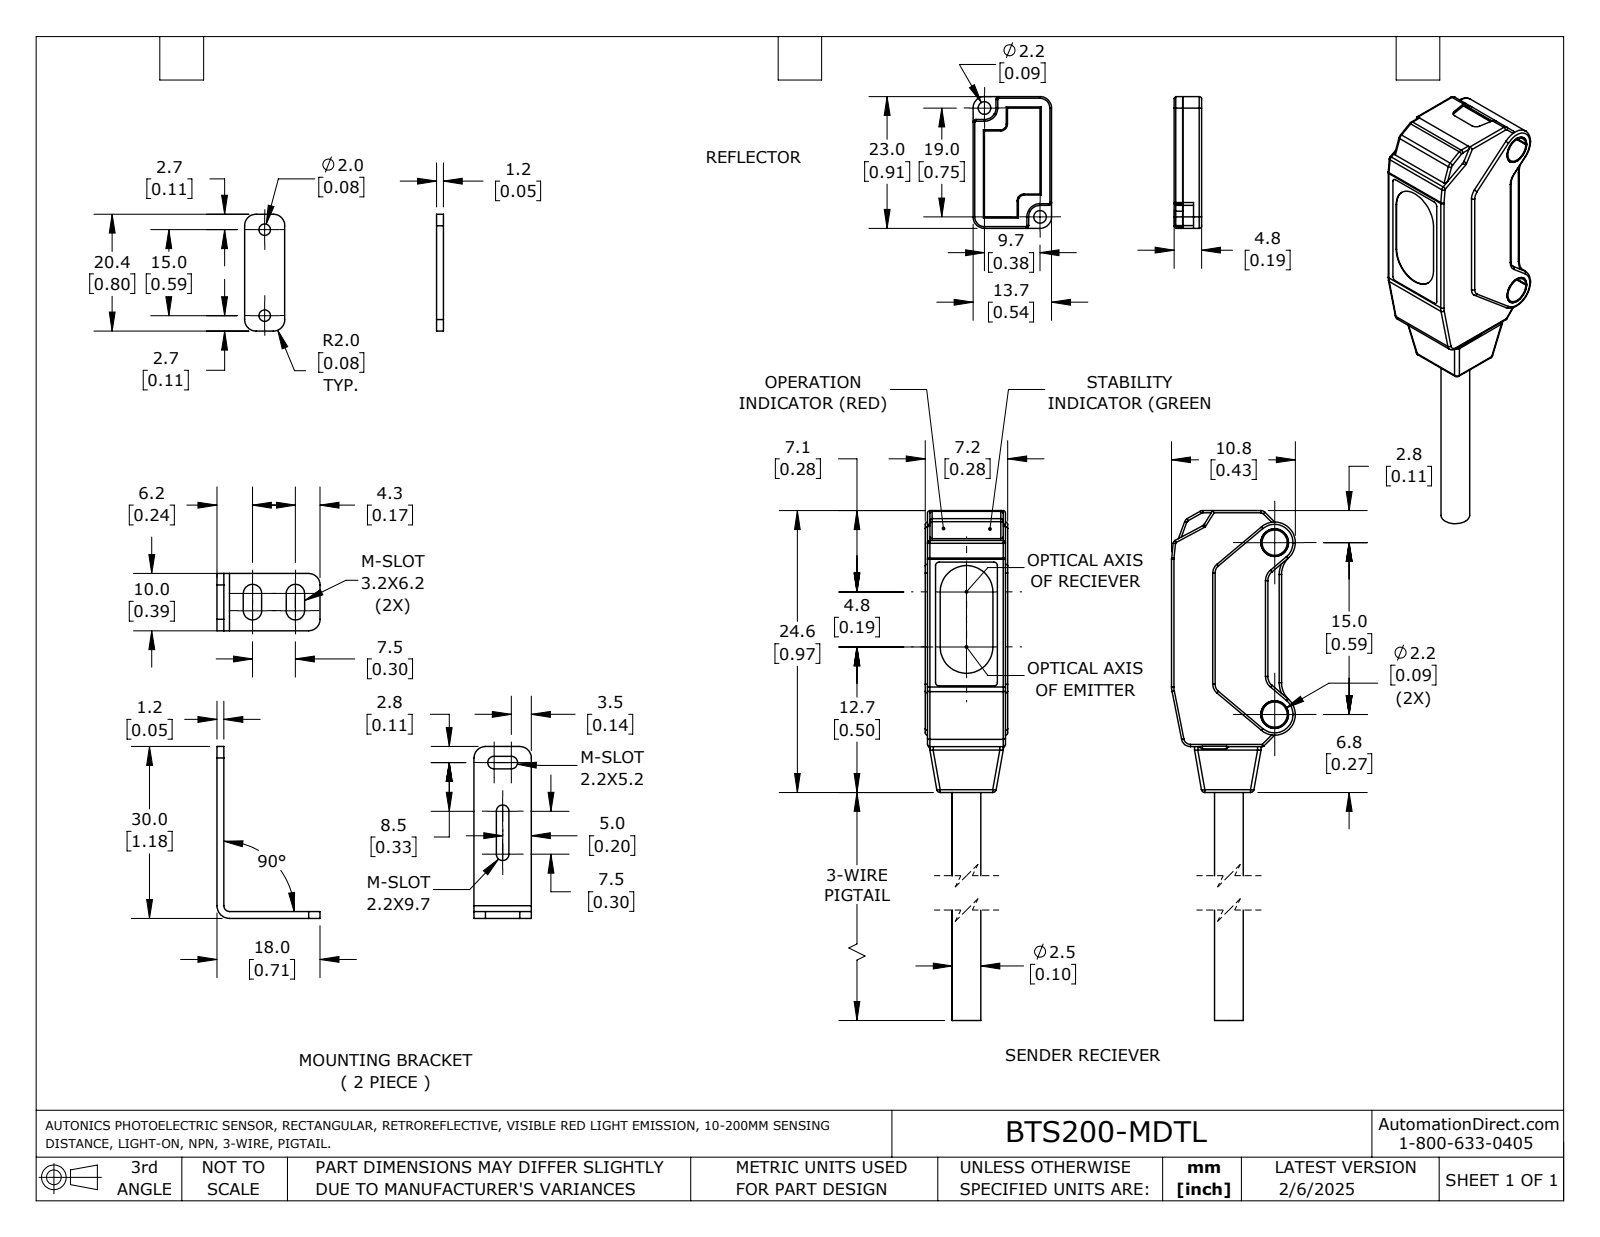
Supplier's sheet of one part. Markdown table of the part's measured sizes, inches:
| quantity | value |
| --- | --- |
| part name | BTS200-MDTL_BTS200-MDTL-P_BTS200-MDTD_BTS200-MDTD-P; BTS200-MDTL_BTS200-MDTL-P_BTS200-MDTD_BTS200-MDTD-P_REFLECTOR; BTS200-MDTL_BTS200-MDTL-P_BTS200-MDTD_BTS200-MDTD-P_SENDER |
| STEP written by | SolidWorks 2024 (AUTOMOTIVE_DESIGN) |
| units | inches |
| bodies | 6 solids, 932 faces (591 planar, 187 cylindrical, 154 other) |
| overall size | 2.74 × 1.641 × 1.134 |
| volume | 0.218 in³ |
| surface area | 5.673 in² |
| round holes (diameter × count) | 0.087 × 4, 0.079 × 2, 0.095 × 2 |
| round bosses / shafts (diameter × count) | 0.157 × 2, 0.094 × 2, 0.098 × 1 |
| partial cylindrical surfaces (radius × count) | 0.008 × 39, 0.079 × 15, 0.012 × 14, 0.02 × 14, 0.063 × 6, 0.008 × 5, 0.016 × 4, 0.019 × 4 |
| main face-to-face distances | 0.047, 0.331, 0.181, 0.276, 0.055, 0.323, 0.283, 0.378, 0.128, 0.081 |
| hole center spacings | 0.591, 0.84 |
